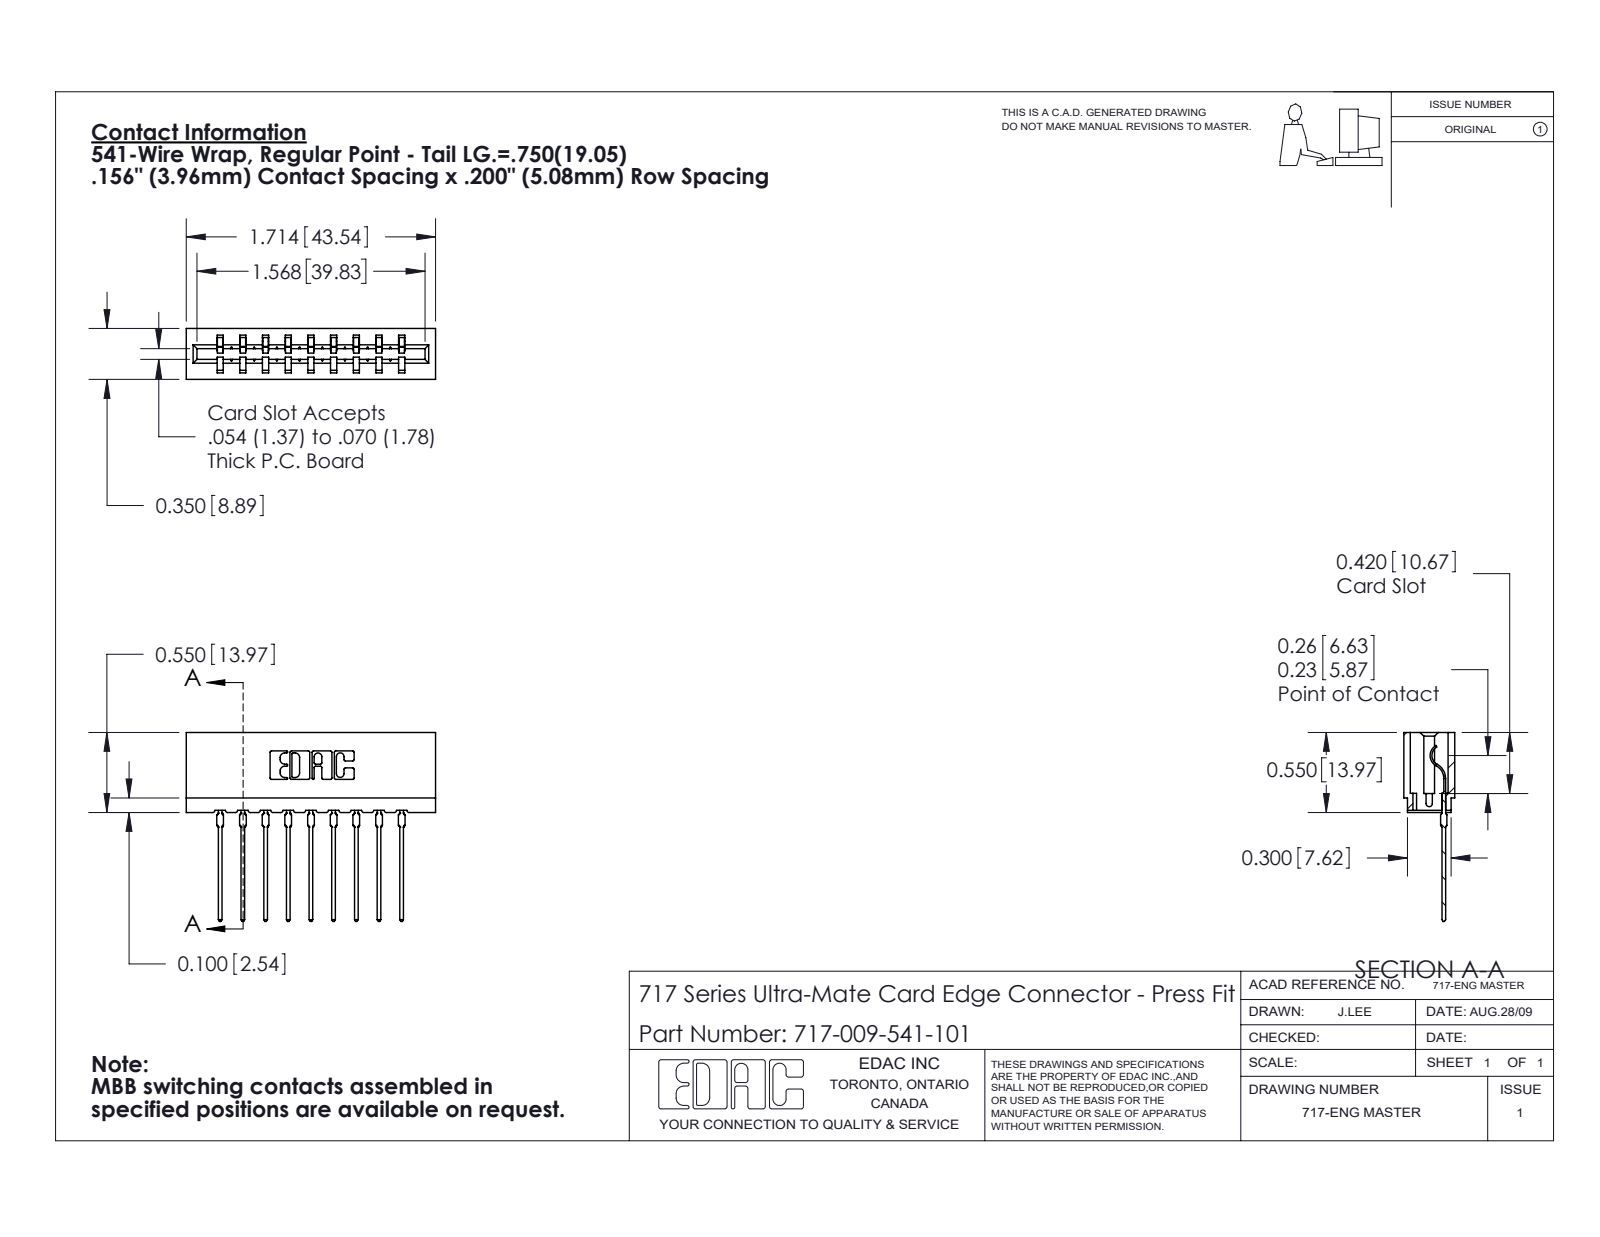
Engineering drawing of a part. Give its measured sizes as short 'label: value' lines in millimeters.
name: 717-009-541-101; 745-292-001_541; 717 Part_Insulator Option - 06
written by: SolidWorks 2020 (CONFIG_CONTROL_DESIGN)
unit: mm
bodies: 10 solids, 1111 faces (666 planar, 211 cylindrical, 234 other)
size: 43.5 × 33 × 8.9
volume: 3 870 mm³; area: 5 259 mm²
rounds: 22× R0.3, 18× R0.4, 18× R0.5, 6× R0.2, 6× R0.8, 4× R0.1, 4× R0.3, 3× R0.7
face distances: 4, 5.4, 15.8, 3.5, 11.9, 5, 8.9, 7.9, 1.1, 7.9
